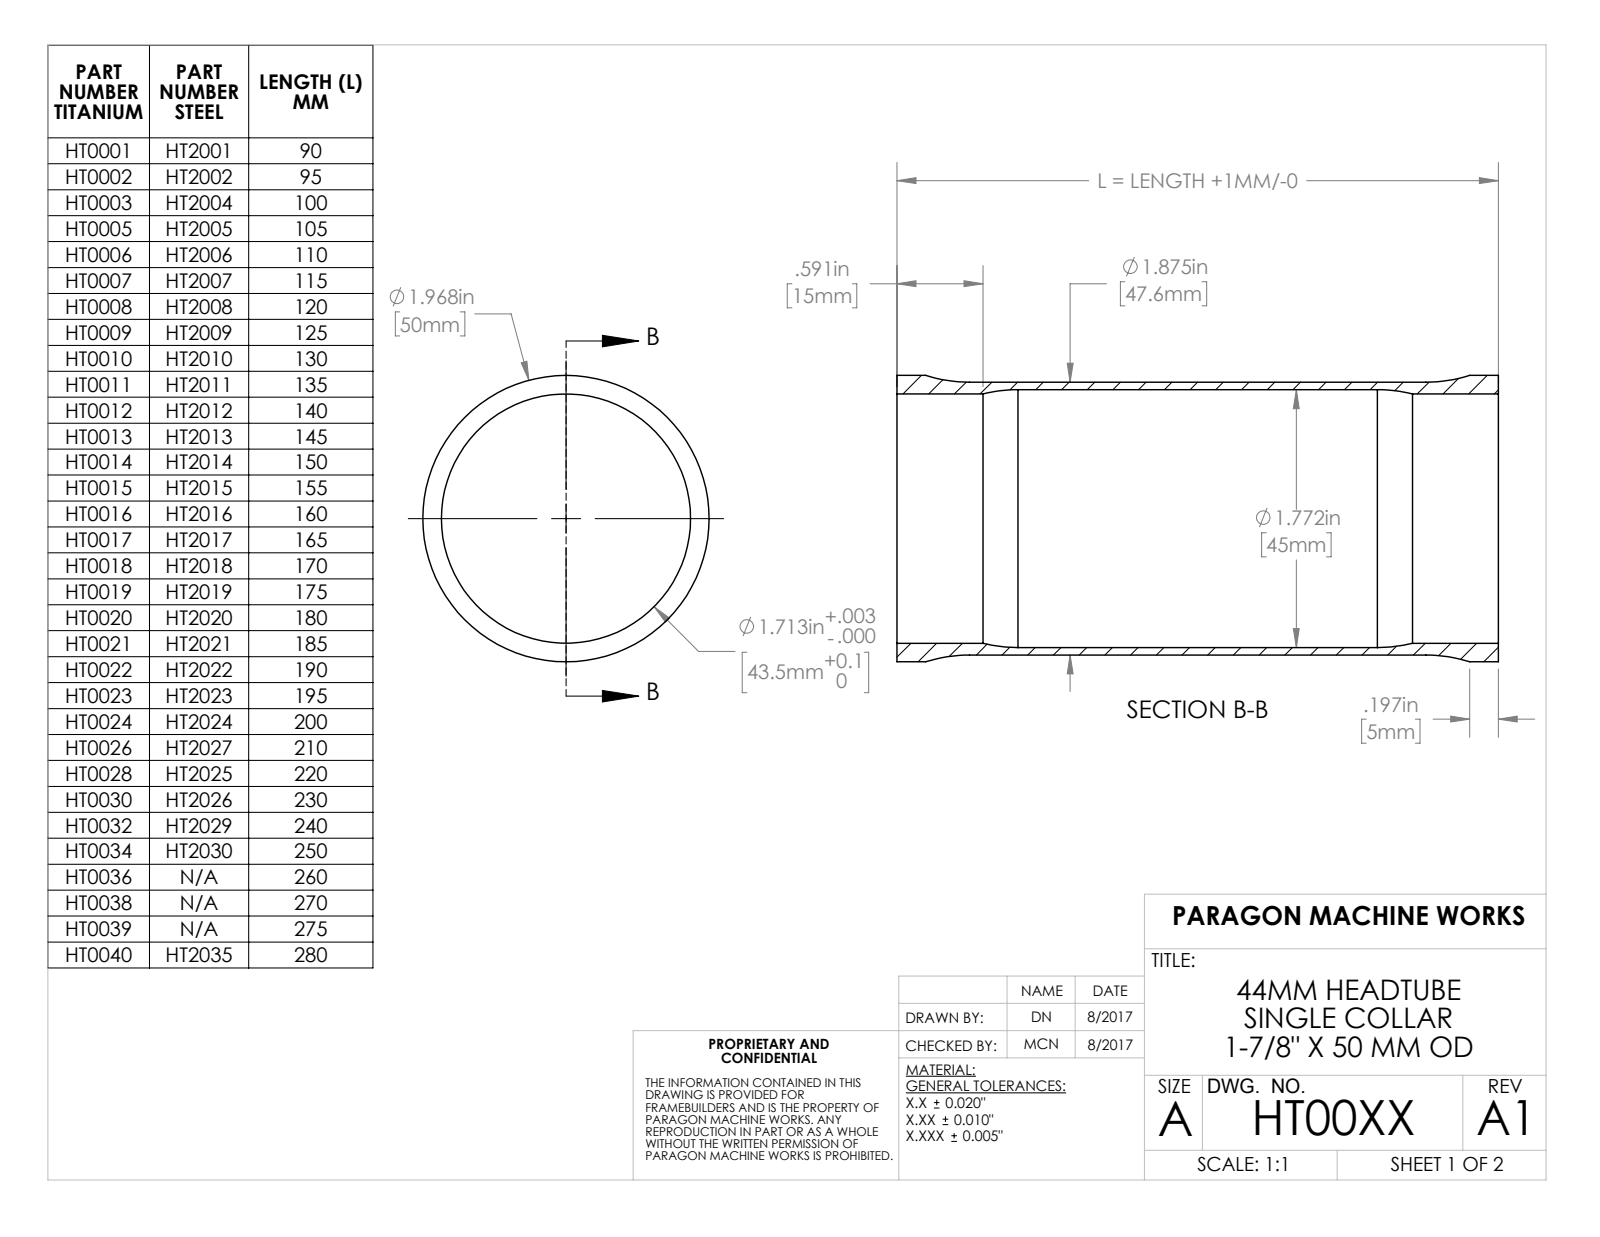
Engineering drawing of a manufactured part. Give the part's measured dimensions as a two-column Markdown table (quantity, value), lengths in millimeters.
| quantity | value |
| --- | --- |
| part name | HT0001 |
| STEP written by | SolidWorks 2012 (CONFIG_CONTROL_DESIGN) |
| units | millimeters |
| bodies | 1 solid, 12 faces (2 planar, 6 cylindrical, 4 other) |
| overall size | 90 × 49.99 × 49.99 |
| volume | 23 401 mm³ |
| surface area | 27 148 mm² |
| round holes (diameter × count) | 43.51 × 1, 45.01 × 1 |
| round bosses / shafts (diameter × count) | 49.99 × 1, 47.62 × 1 |
| main face-to-face distances | 90 |
